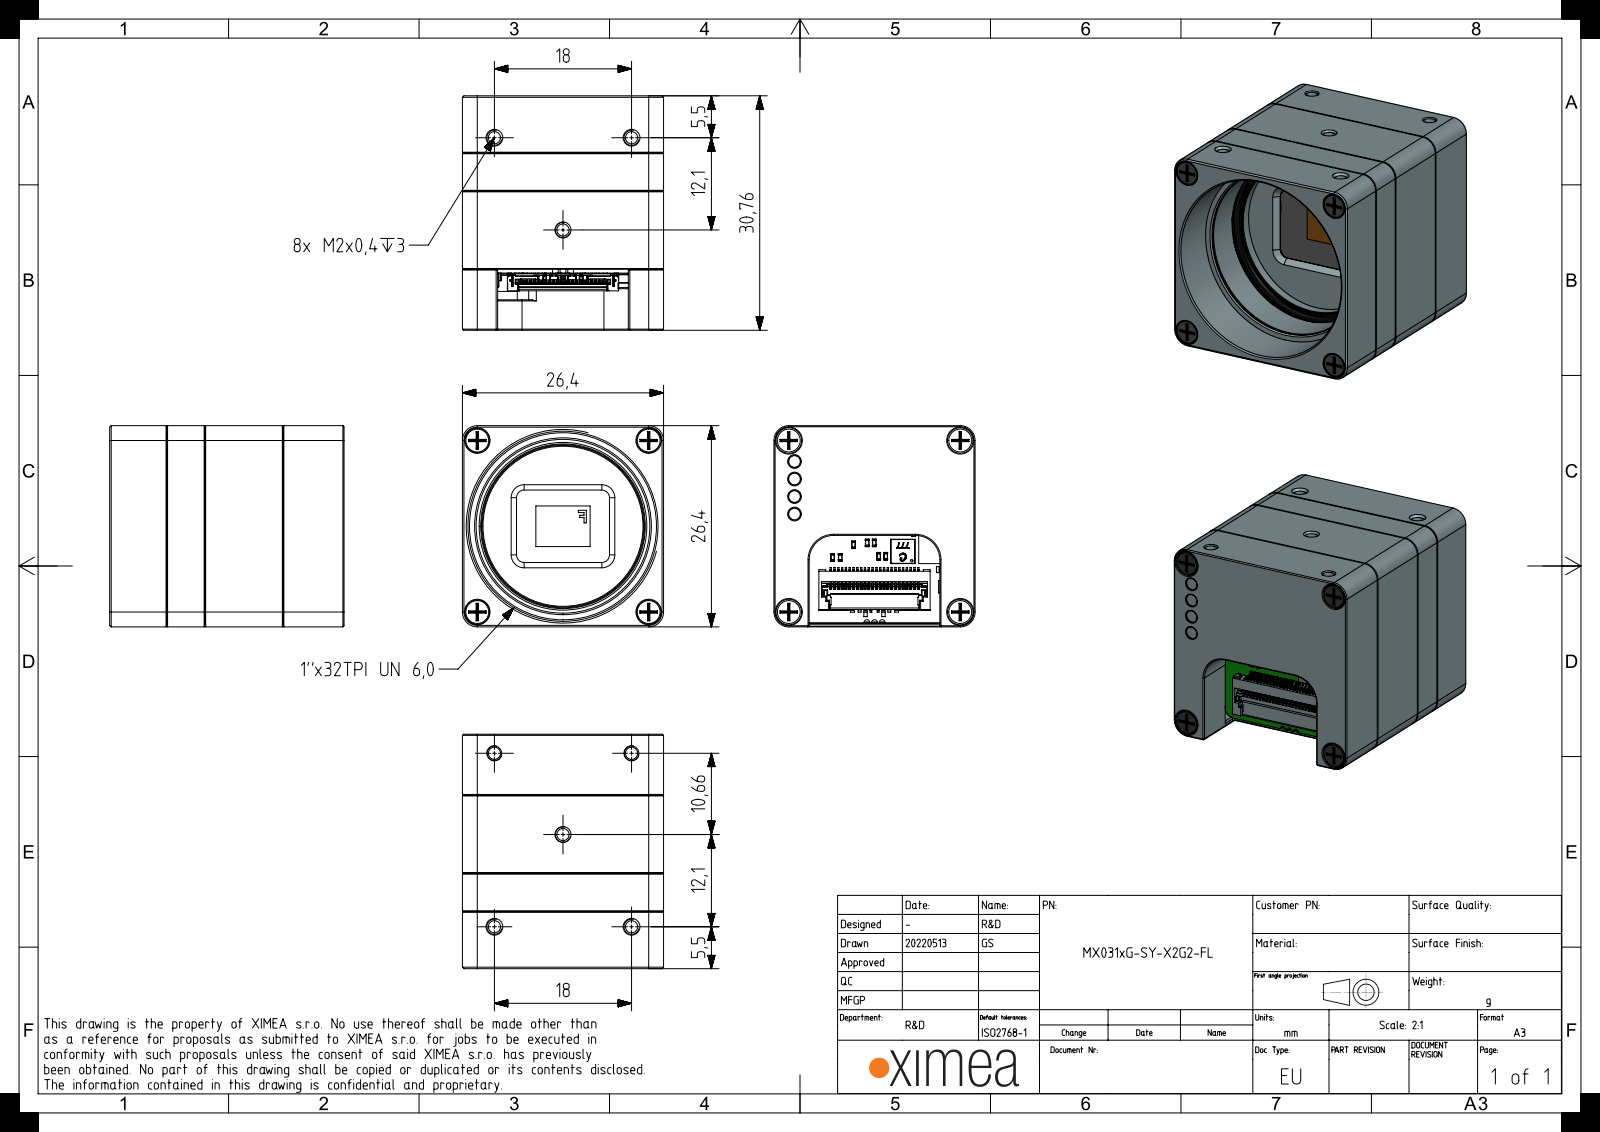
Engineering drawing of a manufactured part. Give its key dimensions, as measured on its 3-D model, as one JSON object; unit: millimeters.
{"part_name": "MX-X2G2-MAIN-FL-PCA; MECH-MX-THERMAL-PAD-10X10; SROB-M2x10-CUST; MECH-LIGHTPIPE-1.63x4.14 (+8 more)", "step_written_by": "SIEMENS PLM Software NX 1907 (AUTOMOTIVE_DESIGN)", "units": "millimeters", "bodies": {"solids": 32, "faces": 7540, "planar": 5180, "cylindrical": 2089, "other": 271}, "overall_size": [30.8, 26.4, 26.4], "volume_mm3": 10300, "surface_area_mm2": 16970, "round_holes": [[1.6, 13], [0.9, 4], [1.8, 4], [2, 4], [2.1, 4], [3, 4], [3.2, 4], [3.4, 4], [1.3, 2], [1.9, 1], [1.9, 1], [21, 1]], "round_bosses_or_shafts": [[1.9, 4], [1.6, 4], [0.8, 4], [3, 2], [1.6, 2], [25, 1], [21.6, 1]], "partial_cylinders_radius": [[1.5, 19], [0.3, 17], [0.1, 14], [0.2, 14], [1, 14], [0.4, 12], [0.2, 10], [1.3, 8]], "face_to_face_distances": [1, 26.4, 3.5, 11.4, 6.9, 7.7, 4.2, 4.5, 6.8, 10.4], "hole_center_spacings": [3.8, 12.9, 15.9, 18.8, 22.1, 22.5, 28.7, 2.3]}
